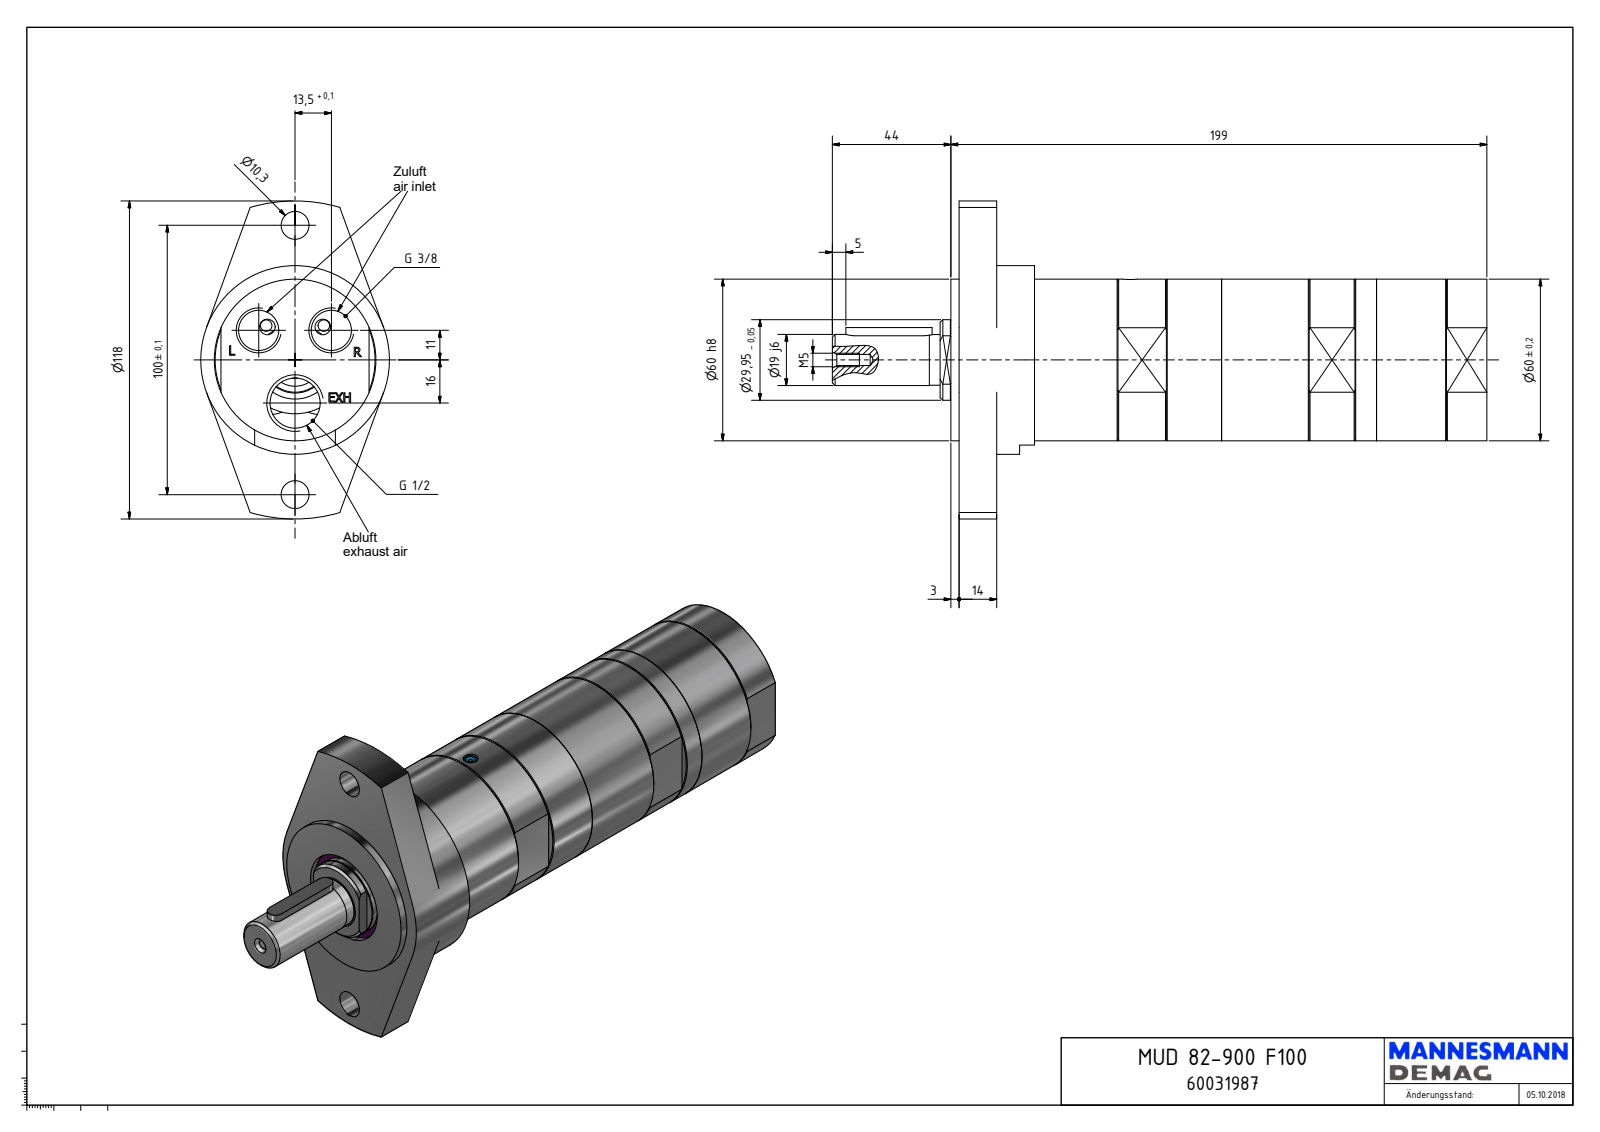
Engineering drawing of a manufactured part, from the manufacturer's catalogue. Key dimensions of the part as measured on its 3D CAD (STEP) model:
Part name (STEP PRODUCT): MUD 82-900_60031987
STEP written by: Autodesk Inventor 2018 (AUTOMOTIVE_DESIGN)
Units: millimetres
Bodies: 1 solid, 204 faces (115 planar, 47 cylindrical, 42 other)
Overall size (bounding box): 243 × 118 × 70
Volume: 616 477 mm³ · Surface area: 61 555 mm²
Round holes (diameter × count): ⌀10.3 ×2, ⌀14.95 ×2, ⌀1.55 ×1, ⌀4 ×1, ⌀4.13 ×1, ⌀5.5 ×1, ⌀18.63 ×1, ⌀35 ×1, ⌀40 ×1
Round bosses / shafts (diameter × count): ⌀70 ×1, ⌀60 ×1, ⌀29.95 ×1, ⌀19 ×1, ⌀18.8 ×1, ⌀5 ×1, ⌀3.6 ×1
Partial cylindrical surfaces — rounded edges, fillets, slot ends (radius × count): R3 ×2, R7.5 ×2, R8.5 ×1, R19.03 ×1, R23.5 ×1, R25.67 ×1, R30.65 ×1, R59 ×1
Main face-to-face distances: 14, 17, 3, 196, 182, 199, 55, 31, 28, 168
Hole centre spacings: 17.41, 30.19, 41.27, 50, 62.48, 16, 27, 34
